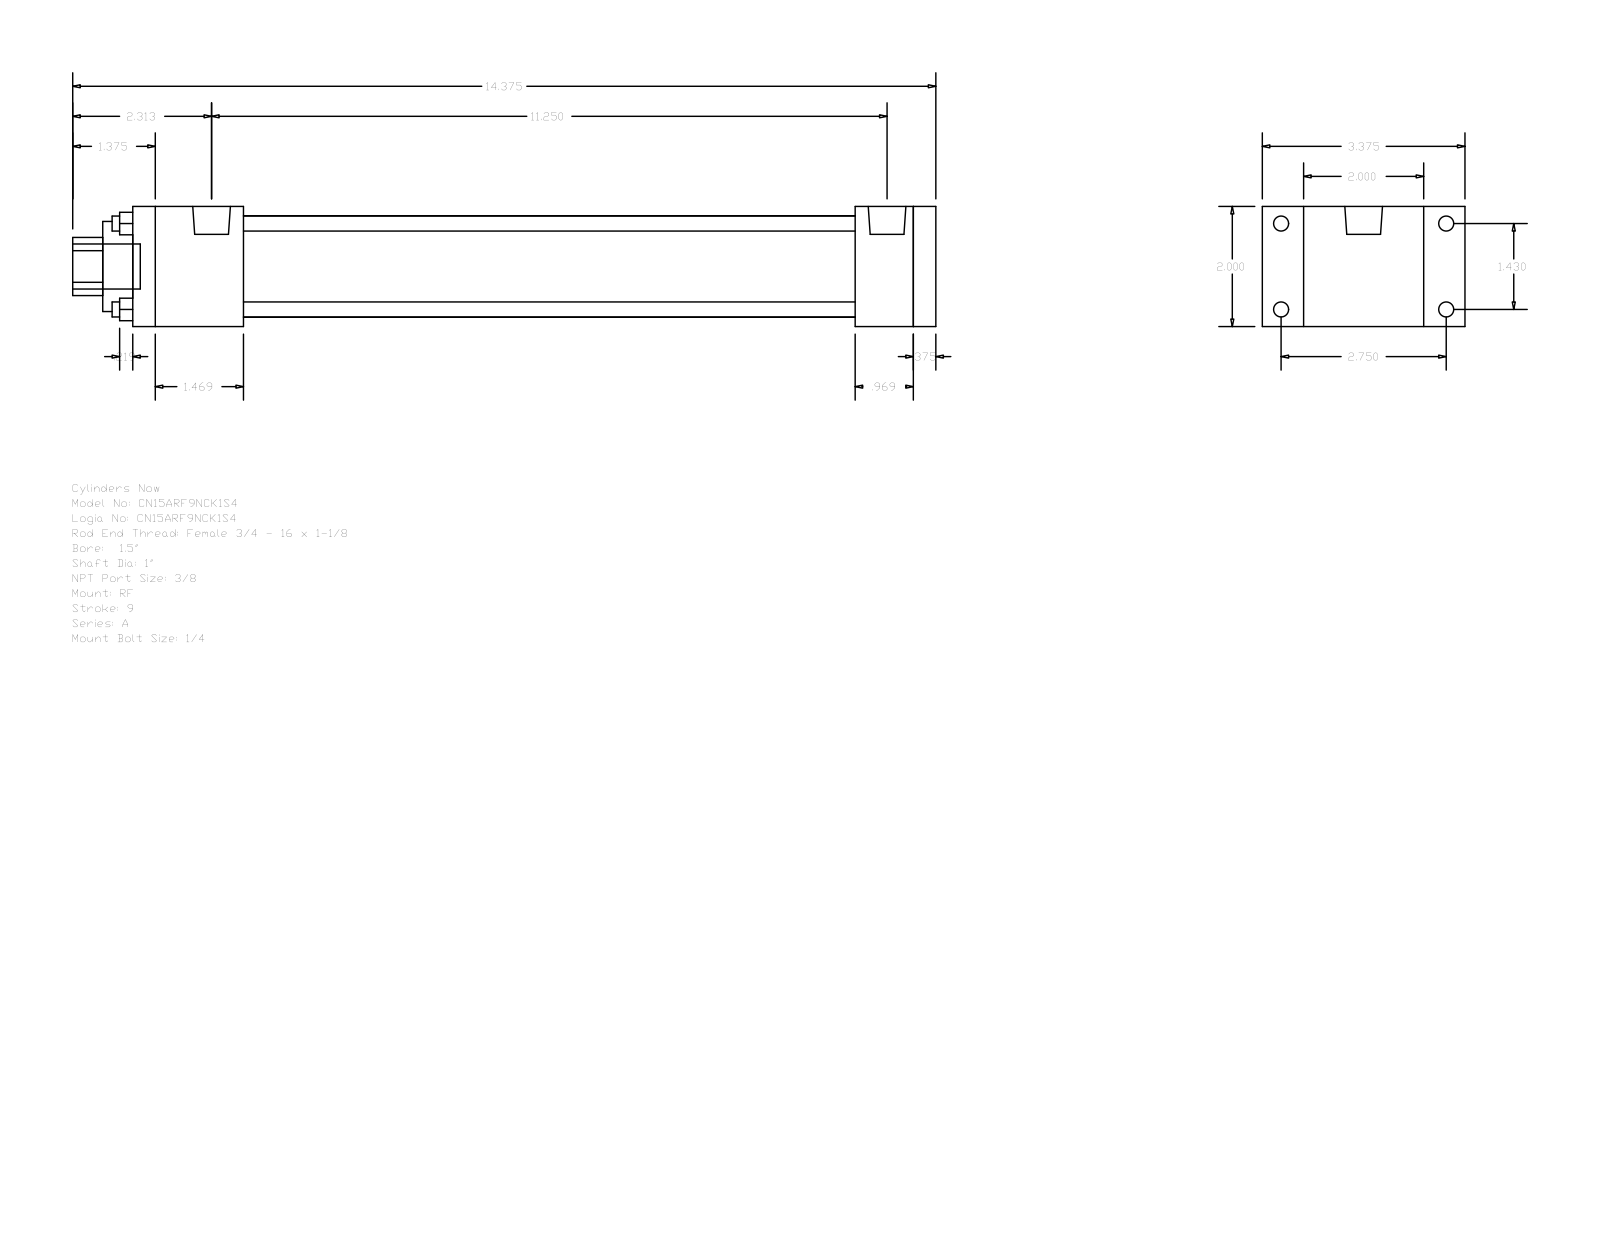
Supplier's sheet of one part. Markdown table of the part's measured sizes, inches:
| quantity | value |
| --- | --- |
| part name | A_RF__0150_1 |
| STEP written by | GSSL Pune (CONFIG_CONTROL_DESIGN) |
| units | inches |
| bodies | 0 solids, 92 faces (64 planar, 28 cylindrical, 0 other) |
| overall size | 14.375 × 3.375 × 2 |
| round holes (diameter × count) | 0.25 × 4, 1 × 1, 1.5 × 1, 1.69 × 1 |
| round bosses / shafts (diameter × count) | 0.25 × 4, 0.219 × 4, 0.627 × 2, 0.75 × 1 |
| partial cylindrical surfaces (radius × count) | 0.484 × 1 |
| main face-to-face distances | 2, 0.375, 13, 13.375, 12.031, 0.969, 1.344, 1.844, 10.187, 11.156 |
| hole center spacings | 1.011, 1.43, 2.022 |
